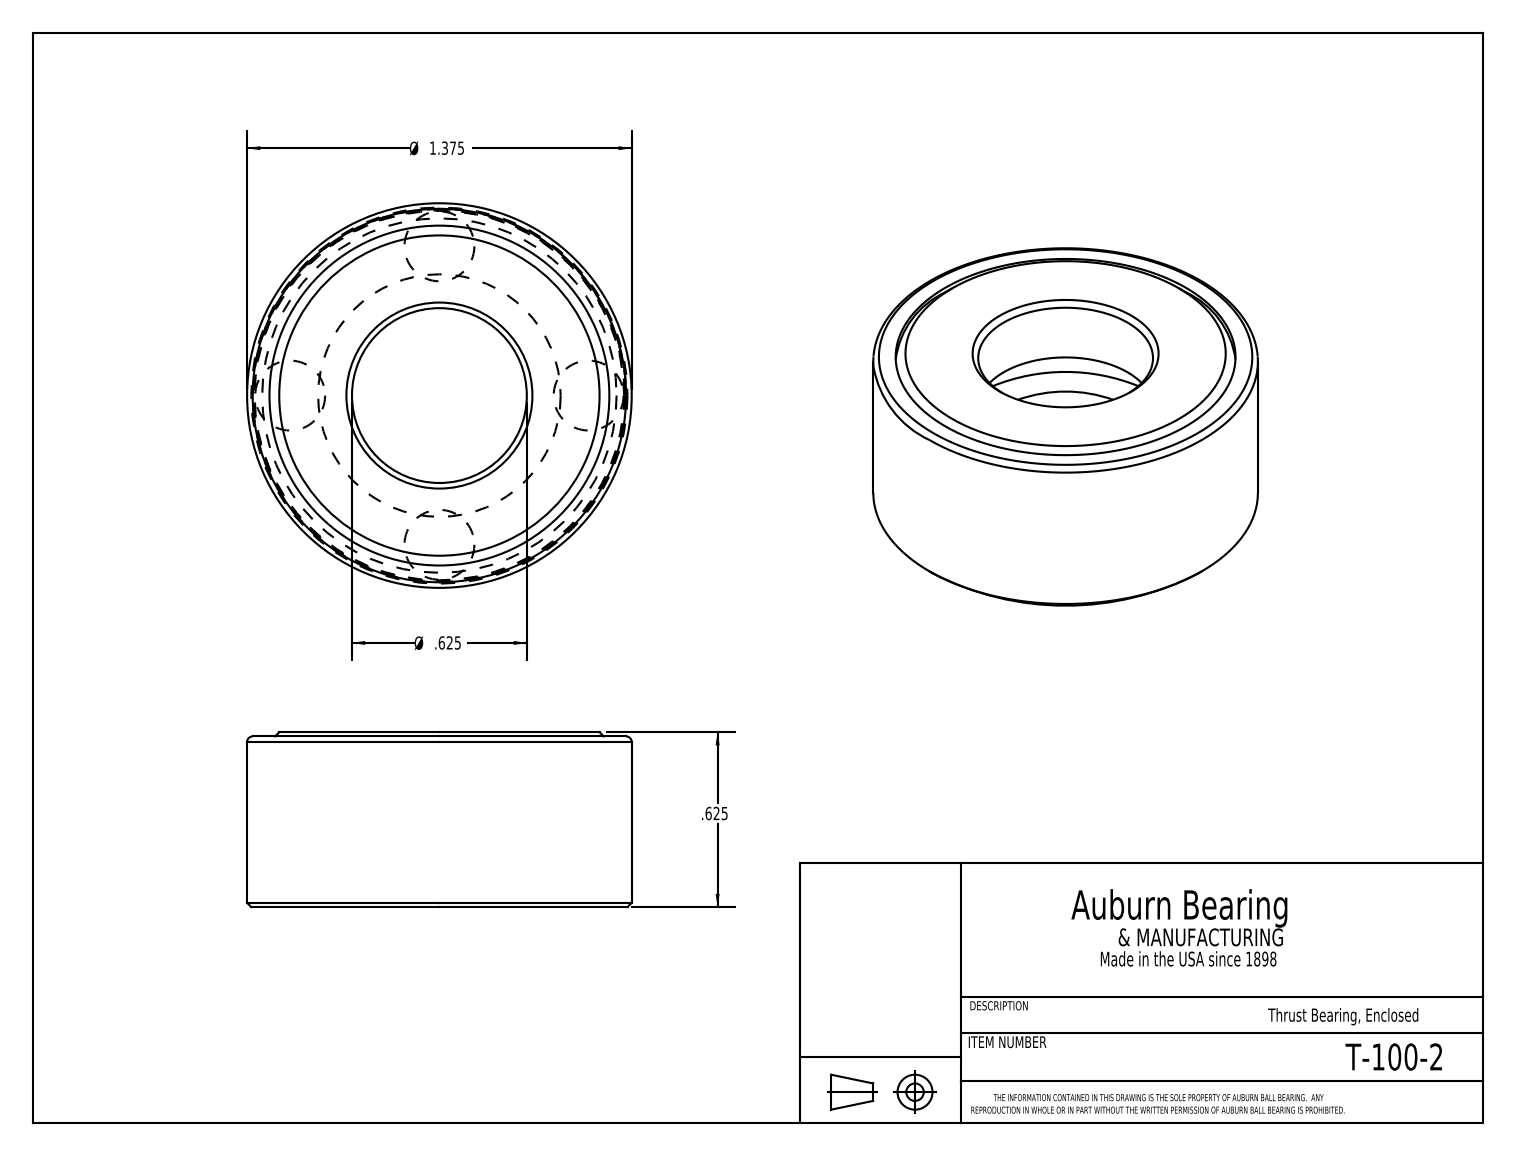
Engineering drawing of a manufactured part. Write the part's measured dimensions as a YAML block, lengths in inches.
part_name: "T-100-2"
step_written_by: "SolidWorks 2016 (CONFIG_CONTROL_DESIGN)"
units: inches
bodies: {solids: 6, faces: 28, planar: 9, cylindrical: 7, other: 12}
overall_size: [1.375, 1.375, 0.625]
volume: 0.538
surface_area: 11.76
round_holes:
  - {diameter: 0.625, count: 1}
  - {diameter: 1.215, count: 1}
  - {diameter: 1.335, count: 1}
round_bosses_or_shafts:
  - {diameter: 1.375, count: 1}
  - {diameter: 1.321, count: 1}
face_to_face_distances: [0.625, 0.237, 0.388, 0.387, 0.15, 0.238, 0.59, 0.61, 0.353, 0.372]
